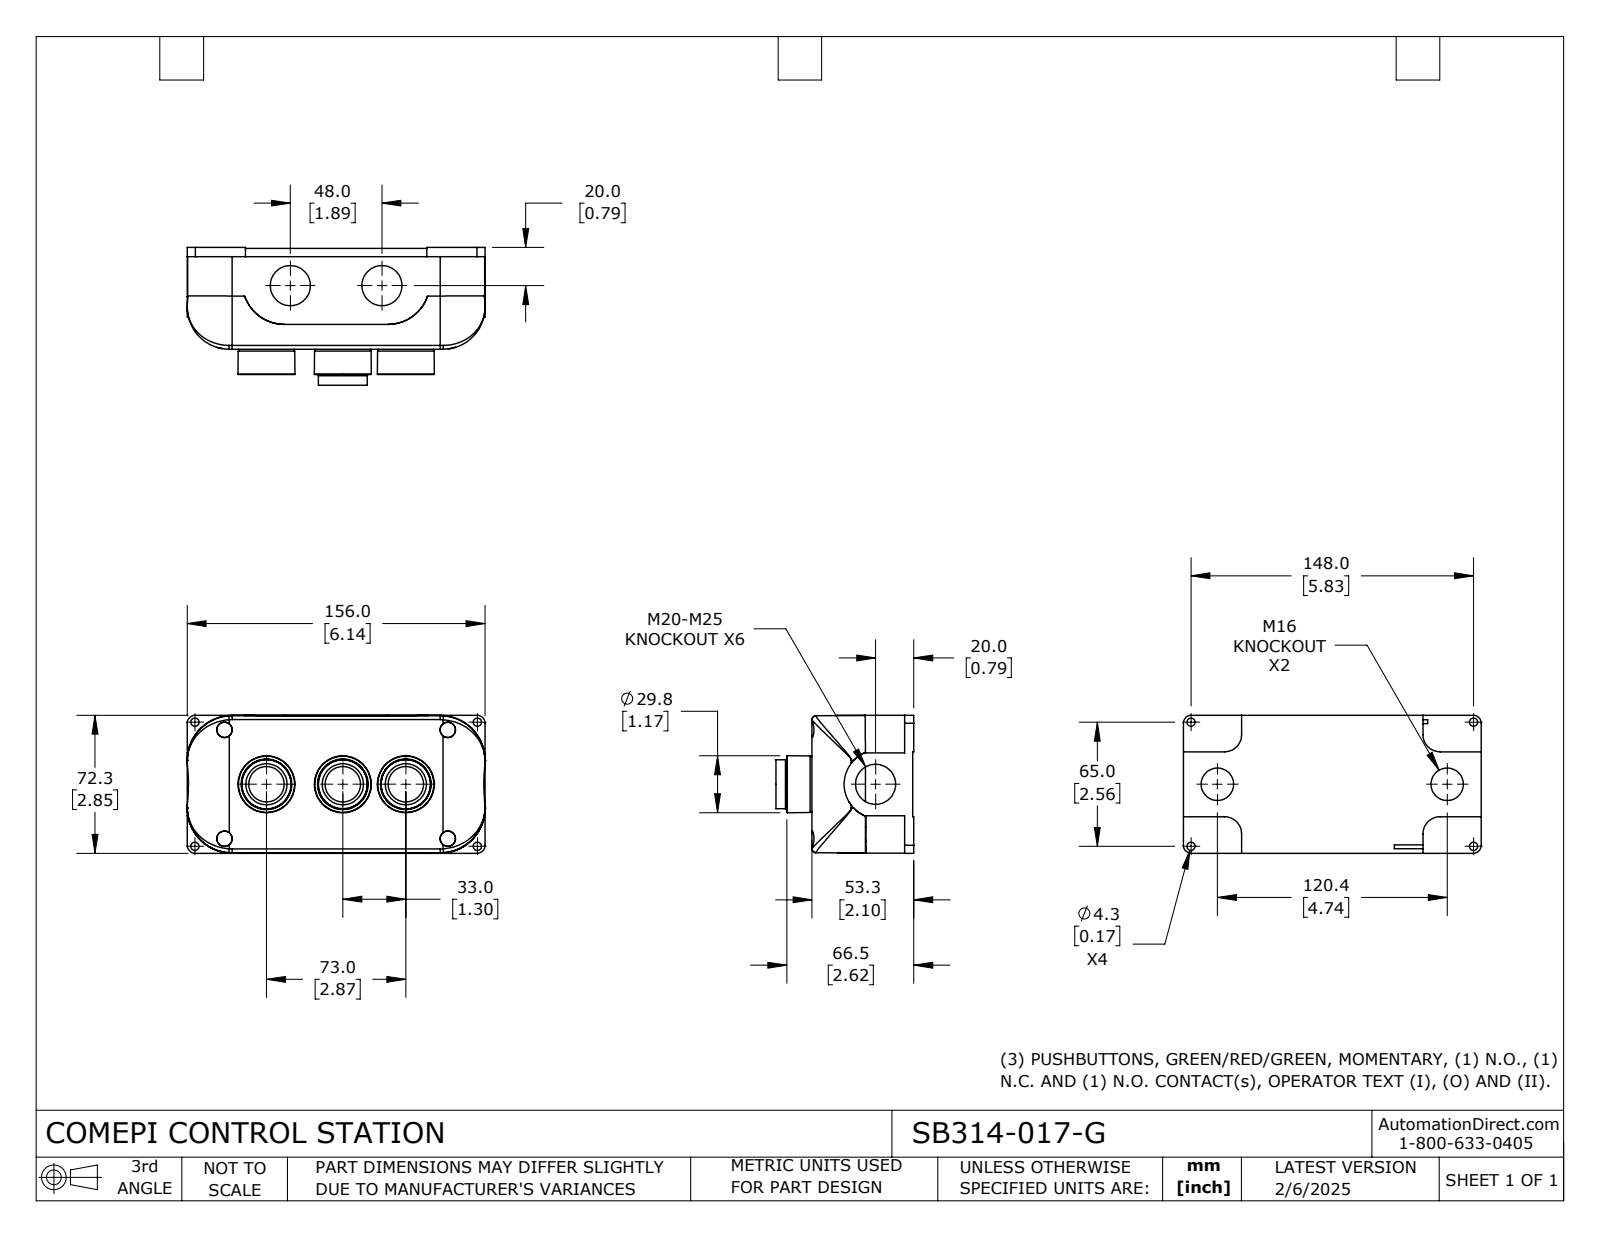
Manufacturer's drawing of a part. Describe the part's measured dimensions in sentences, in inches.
The part is named "SB314-017-G". Its 3-D file was written by "SolidWorks 2024 (CONFIG_CONTROL_DESIGN)". It is 10 solids with 528 faces: 218 planar, 146 cylindrical and 164 other. Overall it measures 6.142 by 2.846 by 2.843 inches. Its volume is 19.43 cubic inches and its surface area 159.5 square inches. Round holes: 4 of diameter 0.169, 3 of diameter 0.531, 3 of diameter 0.827, 3 of diameter 0.854, 2 of diameter 0.669, 1 of diameter 0.713, 1 of diameter 0.89. Round bosses or shafts: 3 of diameter 1.142, 3 of diameter 0.748, 3 of diameter 0.63, 3 of diameter 0.614, 2 of diameter 1.016, 1 of diameter 1.02, 1 of diameter 1.008, 1 of diameter 0.728. Partial cylindrical surfaces (rounded edges, fillets, slot ends): 6 of radius 0.01, 4 of radius 0.035, 4 of radius 0.079, 4 of radius 0.157, 4 of radius 0.354, 4 of radius 0.38, 4 of radius 0.866, 4 of radius 0.93. The main face-to-face distances are 0.098, 2.079, 1.98, 0.118, 0.512, 1.567, 1.469, 0.591, 1.102, 0.976. The hole center spacings are 1.39, 1.954, 4.535, 5.436, 0.933, 2.559, 3.056, 3.309.
